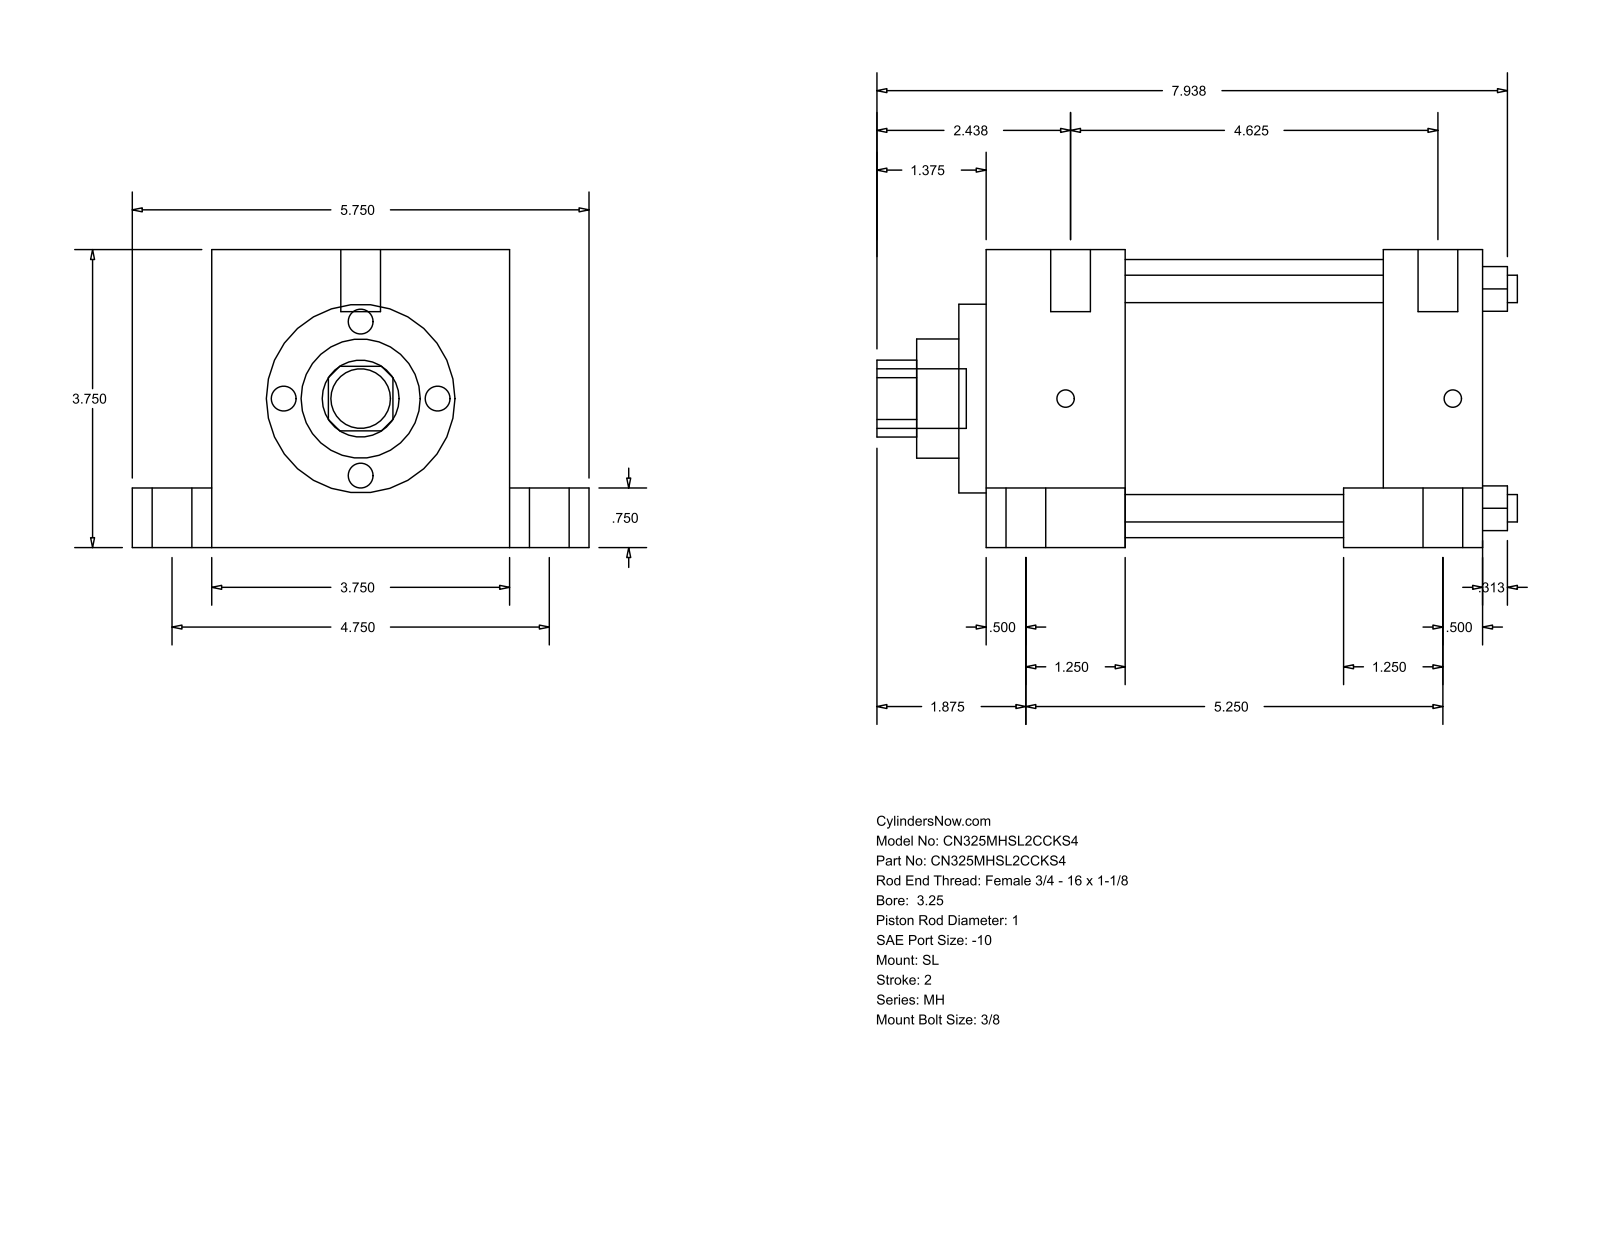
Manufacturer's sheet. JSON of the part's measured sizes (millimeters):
{"part_name": "MH_SL__0325_1", "step_written_by": "GSSL Pune (CONFIG_CONTROL_DESIGN)", "units": "millimeters", "bodies": {"solids": 0, "faces": 110, "planar": 77, "cylindrical": 33, "other": 0}, "overall_size": [204.79, 146.05, 95.25], "round_holes": [[8.76, 4], [25.4, 1], [38.1, 1], [60.33, 1], [88.9, 1]], "round_bosses_or_shafts": [[12.7, 6], [19.05, 5], [5.56, 4]], "partial_cylinders_radius": [[12.29, 1]], "face_to_face_distances": [95.24, 158.76, 44.46, 114.3, 120.65, 25.41, 19.05, 76.19, 127.01, 82.55], "hole_center_spacings": [49.57, 70.1, 99.14]}
